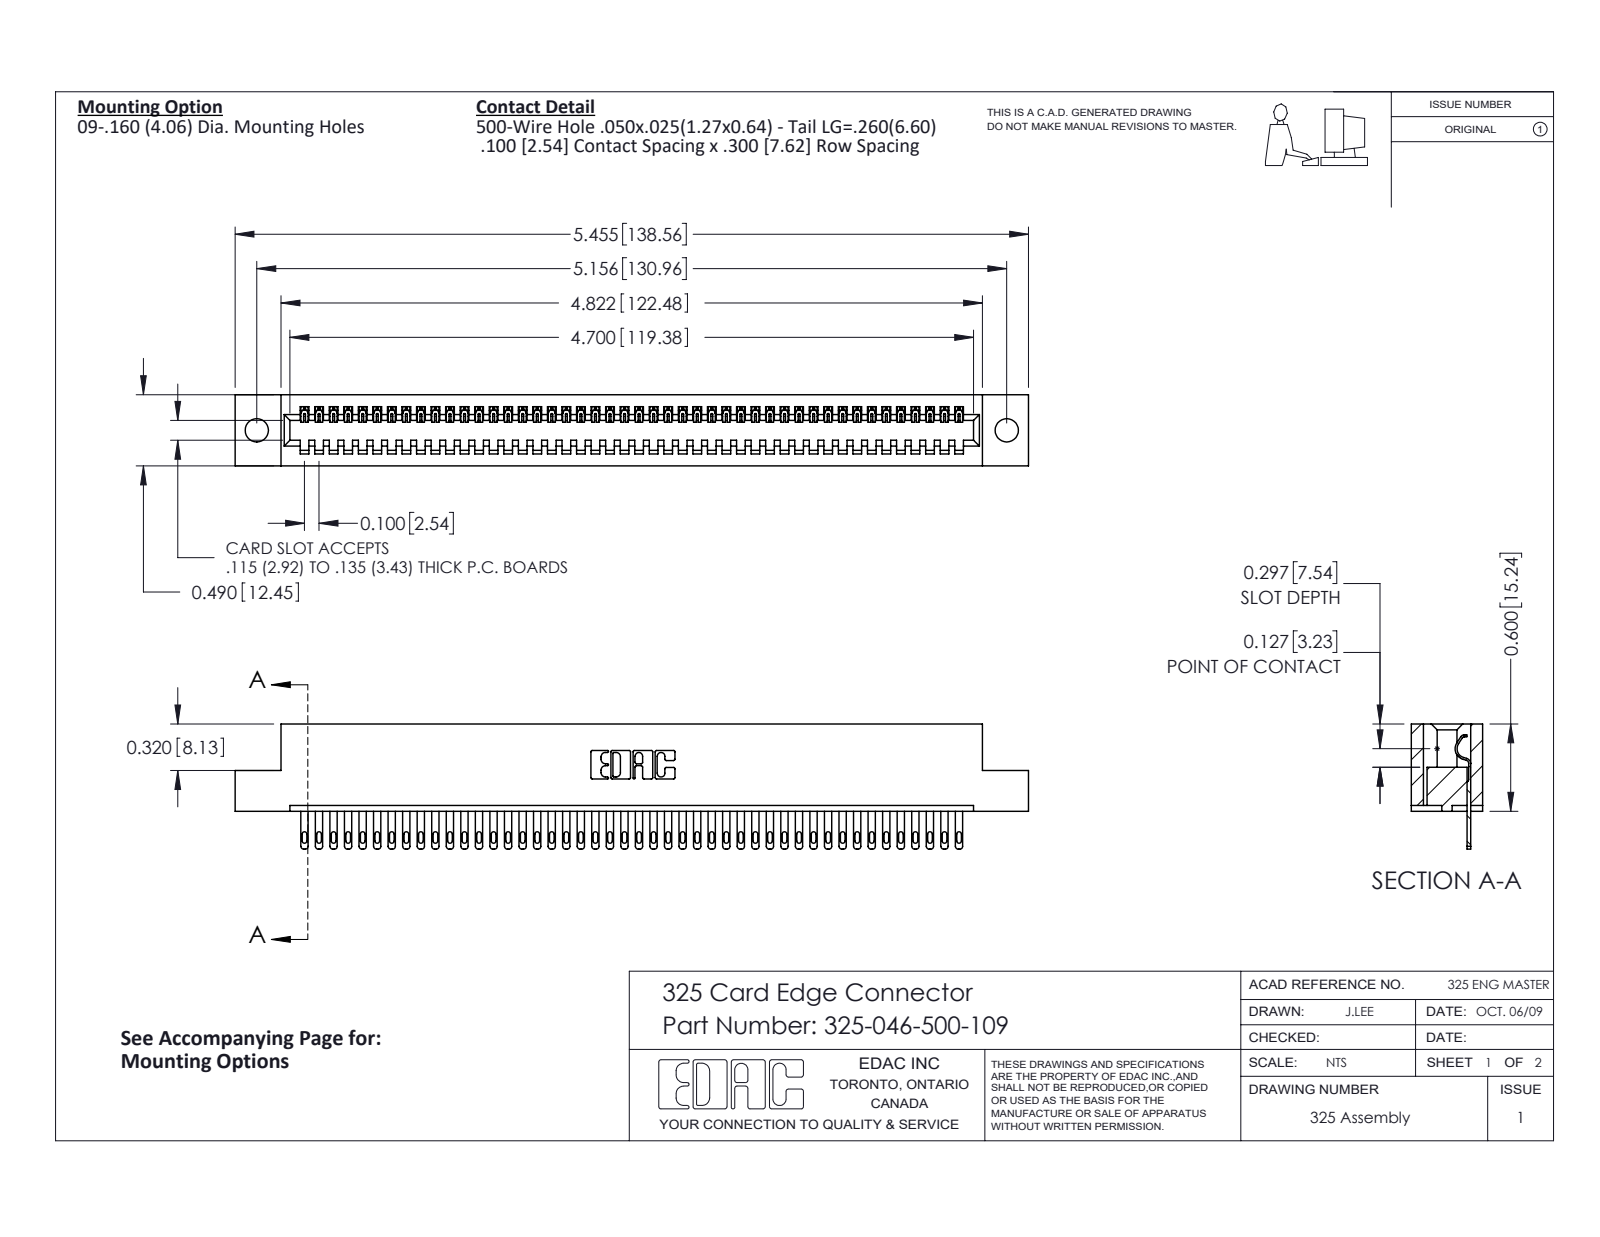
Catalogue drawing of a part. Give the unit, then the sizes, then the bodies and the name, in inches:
Units: inches
Overall size (bounding box): 5.455 × 0.86 × 0.49
Round holes (diameter × count): ⌀0.16 ×2
Partial cylindrical surfaces — rounded edges, fillets, slot ends (radius × count): R0.006 ×92, R0.016 ×92, R0.02 ×92, R0.01 ×22, R0.007 ×6, R0.031 ×6, R0.026 ×3, R0.014 ×1
Main face-to-face distances: 0.083, 0.407, 0.49, 0.3, 0.107, 0.383, 0.025, 0.325, 0.56, 0.263
Hole centre spacings: 5.156
Volume: 1.063 in³ · Surface area: 29.61 in²
Bodies: 47 solids, 2598 faces (1726 planar, 872 cylindrical, 0 other)
Part name (STEP PRODUCT): 325-292-001_325-293-100; 325-046-500-109; 325 Part_.160 TH
STEP written by: SolidWorks 2016 (CONFIG_CONTROL_DESIGN)
